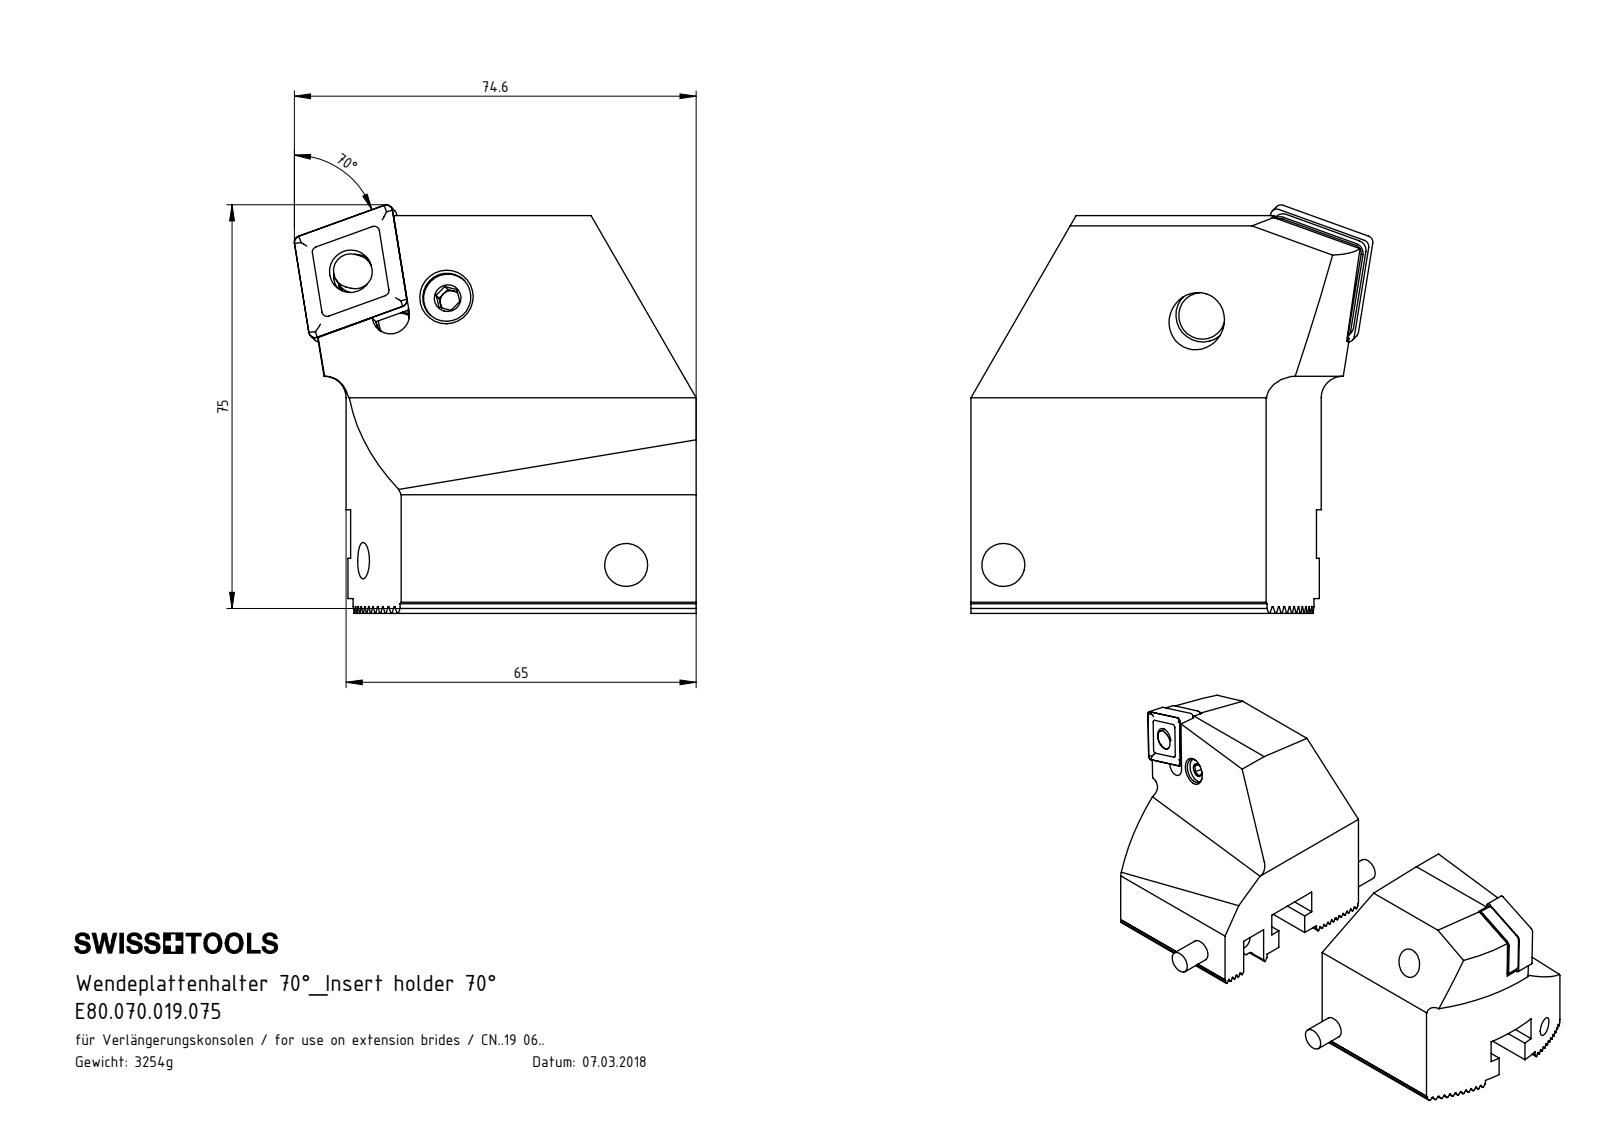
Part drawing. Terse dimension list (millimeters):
name: ISO 4028 - M8 x 35; CNMG190612; WCF-ER2.101.004_A; WCF-ER1.101.000 (+6 more)
written by: SolidWorks 2017 (CONFIG_CONTROL_DESIGN)
unit: mm
bodies: 18 solids, 1312 faces (784 planar, 172 cylindrical, 356 other)
size: 200.21 × 94 × 75.79
volume: 411 183 mm³; area: 74 323 mm²
holes: 4× ⌀8, 2× ⌀6.8, 2× ⌀7.94, 2× ⌀9, 2× ⌀9.6, 2× ⌀10.2
bosses: 2× ⌀10, 2× ⌀9.9, 2× ⌀8.6, 2× ⌀8, 2× ⌀5.5, 2× ⌀4.45
rounds: 22× R0.14, 8× R1.2, 8× R1.8, 8× R4.15, 3× R4.7, 2× R3.1, 2× R3.5, 2× R3.65
face distances: 1.73, 6.93, 8.66, 70, 3.46, 5.2, 41.57, 43.3, 24.5, 45.5
hole spacings: 7, 18.55, 70, 18.8, 18.81, 40, 63, 77
